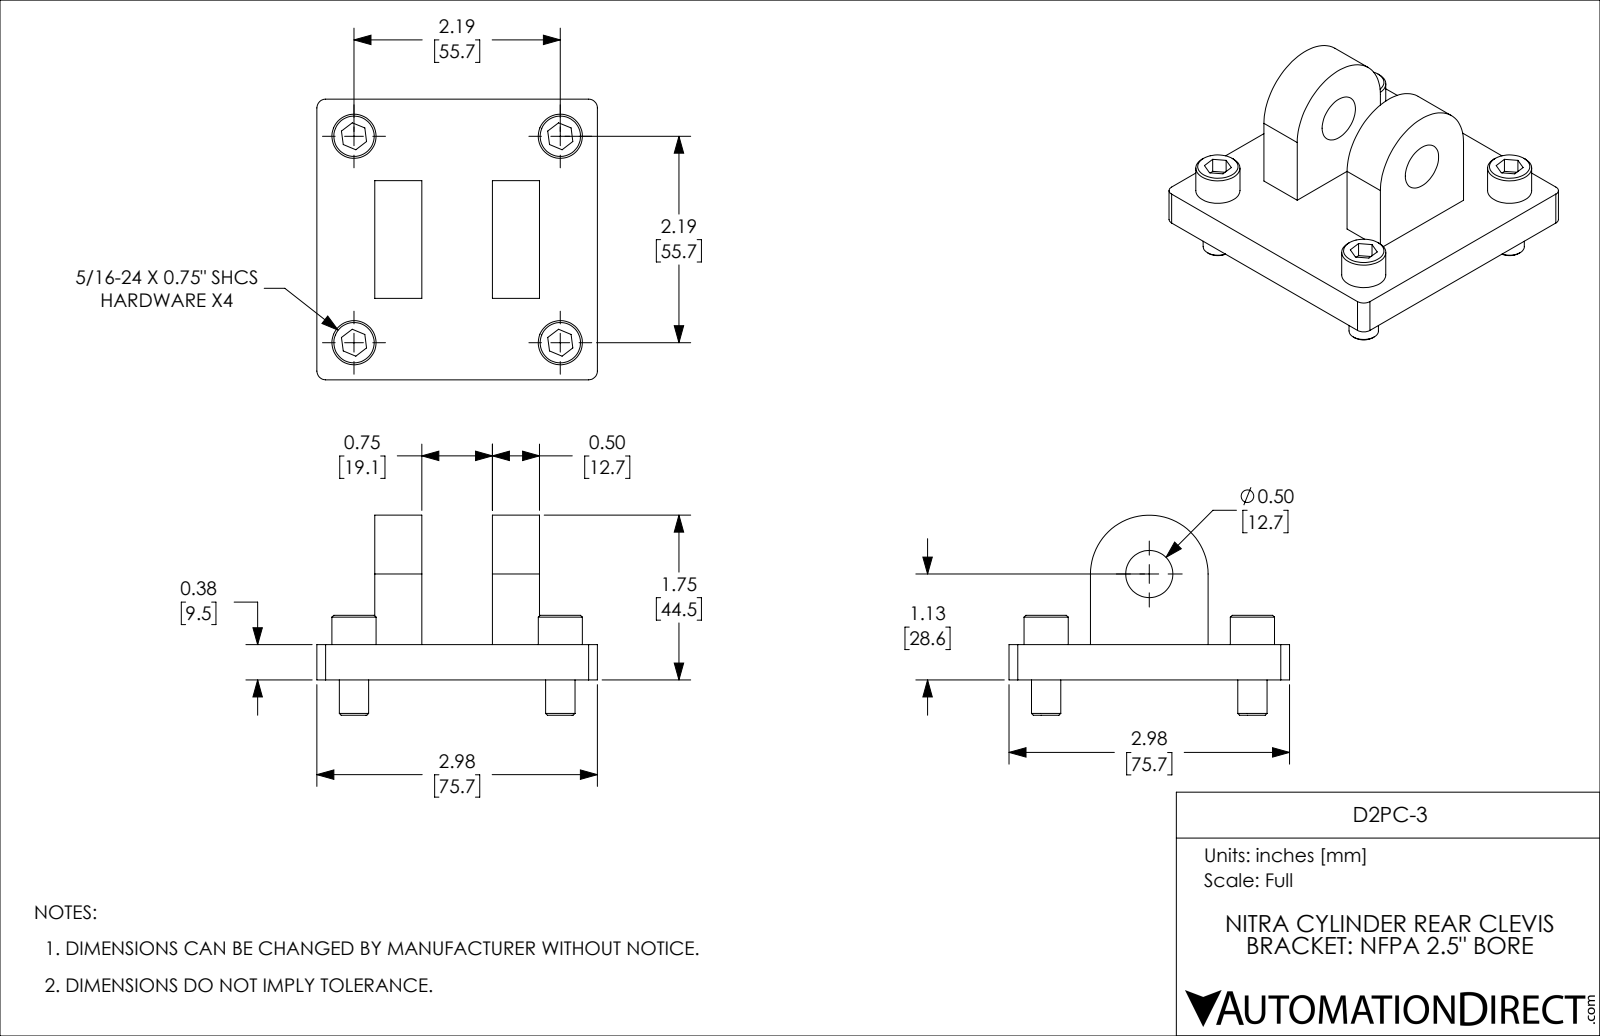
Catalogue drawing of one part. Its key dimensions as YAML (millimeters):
part_name: "D2PC-3"
step_written_by: "SolidWorks 2019 (CONFIG_CONTROL_DESIGN)"
units: millimeters
bodies: {solids: 5, faces: 104, planar: 54, cylindrical: 34, other: 16}
overall_size: [75.7, 75.7, 54]
volume: 81130
surface_area: 25050
round_holes:
  - {diameter: 8.7, count: 4}
  - {diameter: 12.7, count: 1}
round_bosses_or_shafts:
  - {diameter: 11.9, count: 4}
  - {diameter: 7.9, count: 4}
partial_cylinders:
  - {radius: 2.4, count: 4}
  - {radius: 15.9, count: 1}
face_to_face_distances: [9.5, 12.7, 31.8, 75.7, 22, 53.7, 19.1, 44.5, 60.1, 47.4]
hole_center_spacings: [55.7, 78.7]
